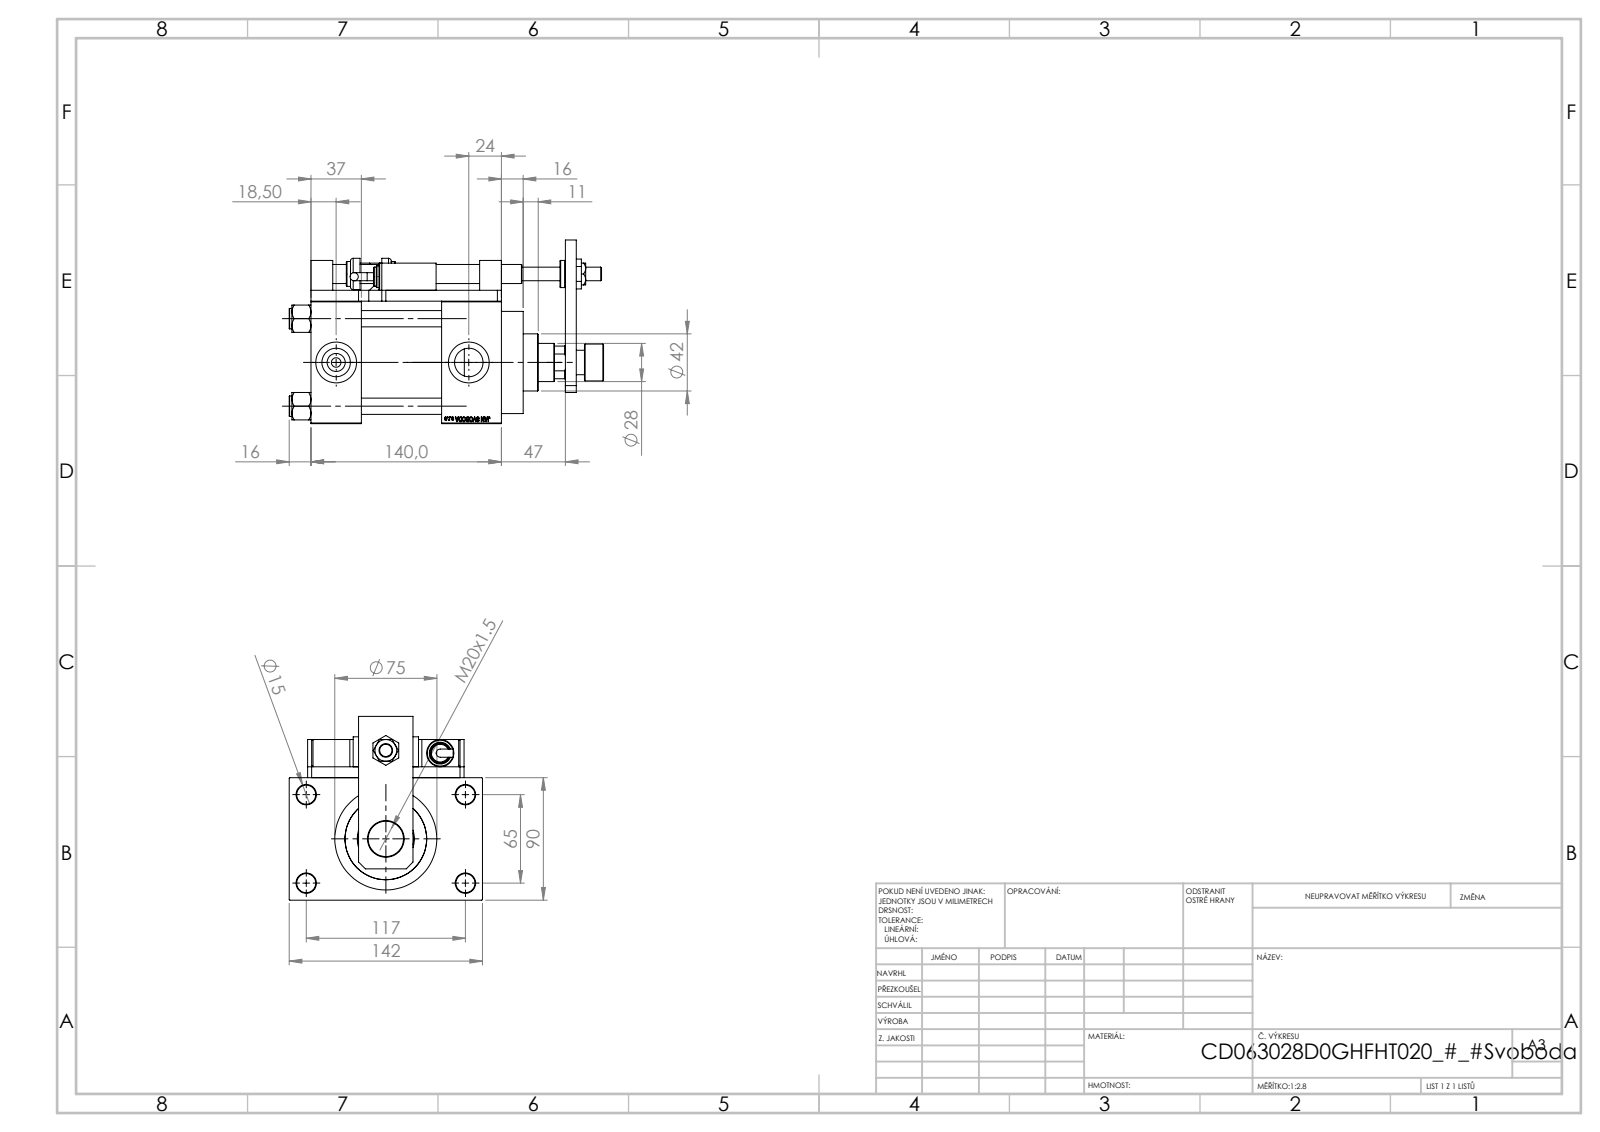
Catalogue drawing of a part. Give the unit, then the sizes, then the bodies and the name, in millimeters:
Units: millimetres
Overall size (bounding box): 231 × 142 × 135
Round holes (diameter × count): ⌀14 ×5, ⌀8.5 ×4, ⌀12 ×4, ⌀13.5 ×4, ⌀7 ×2, ⌀20.96 ×2, ⌀30 ×2, ⌀10 ×1, ⌀18.5 ×1, ⌀20 ×1, ⌀28 ×1, ⌀31 ×1
Round bosses / shafts (diameter × count): ⌀15 ×4, ⌀20 ×3, ⌀16 ×2, ⌀14 ×2, ⌀6 ×2, ⌀75 ×1, ⌀69 ×1, ⌀42 ×1
Partial cylindrical surfaces — rounded edges, fillets, slot ends (radius × count): R7.5 ×4
Main face-to-face distances: 8, 90, 44, 140, 37, 103, 59, 98, 96, 20
Hole centre spacings: 66.92, 26.35, 45.47, 64.3, 69.81, 90.65, 111.34, 65
Volume: 1 373 000 mm³ · Surface area: 288 811 mm²
Bodies: 25 solids, 1345 faces (622 planar, 160 cylindrical, 563 other)
Part name (STEP PRODUCT): V215CD_SWITCH_Q_PODLOZKA_FRONT; V215CD_VCP_D; V215CD_D_TYCINKA; V215CD_SWITCH_Q_ZARAZKA (+8 more)
STEP written by: SolidWorks 2019 (CONFIG_CONTROL_DESIGN)
